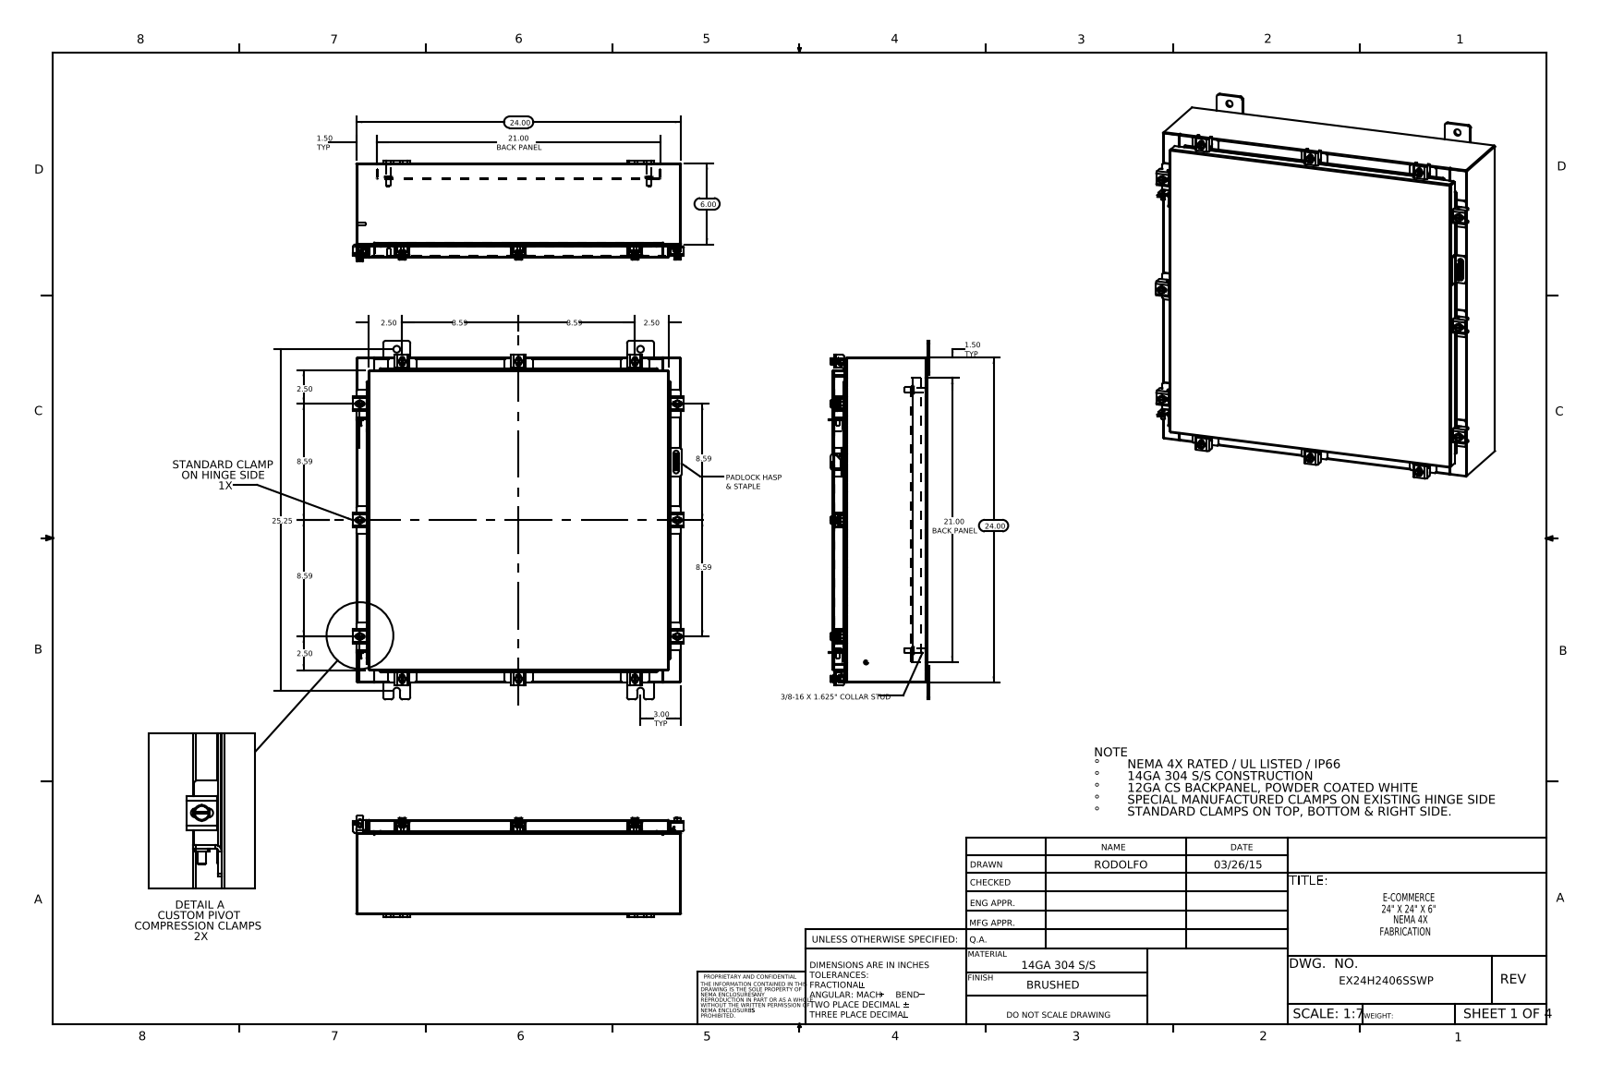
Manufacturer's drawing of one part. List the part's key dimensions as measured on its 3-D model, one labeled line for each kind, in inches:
Part name (STEP PRODUCT): N-WMT04X30402202210-00 Clamp Top; EX24H2406SSWP Cover; EX24H2406SSWP Padlock Hasp; N-WMT04X30402202210-00 22104005_DEFAULT (+8 more)
STEP written by: SolidWorks 2014 (CONFIG_CONTROL_DESIGN)
Units: inches
Bodies: 81 solids, 2018 faces (1075 planar, 783 cylindrical, 160 other)
Overall size (bounding box): 26.5 × 24.421 × 7.453
Volume: 202.2 in³ · Surface area: 5 023 in²
Round holes (diameter × count): ⌀0.213 ×12, ⌀0.26 ×12, ⌀0.5 ×8, ⌀0.125 ×1, ⌀0.25 ×1
Round bosses / shafts (diameter × count): ⌀0.5 ×12, ⌀0.25 ×12, ⌀0.399 ×10, ⌀0.625 ×4, ⌀0.375 ×4, ⌀0.33 ×4, ⌀0.315 ×2, ⌀0.236 ×2
Partial cylindrical surfaces — rounded edges, fillets, slot ends (radius × count): R0.06 ×54, R0.013 ×24, R0.141 ×24, R0.19 ×24, R0.088 ×22, R0.12 ×22, R0.09 ×18, R0.05 ×17
Main face-to-face distances: 0.075, 6.9, 23.925, 6.975, 6.826, 0.104, 1, 1.075, 5.826, 5.9
Hole centre spacings: 8.594, 12.137, 20.559, 23.46, 24.976, 2.34, 18.34, 21.376
